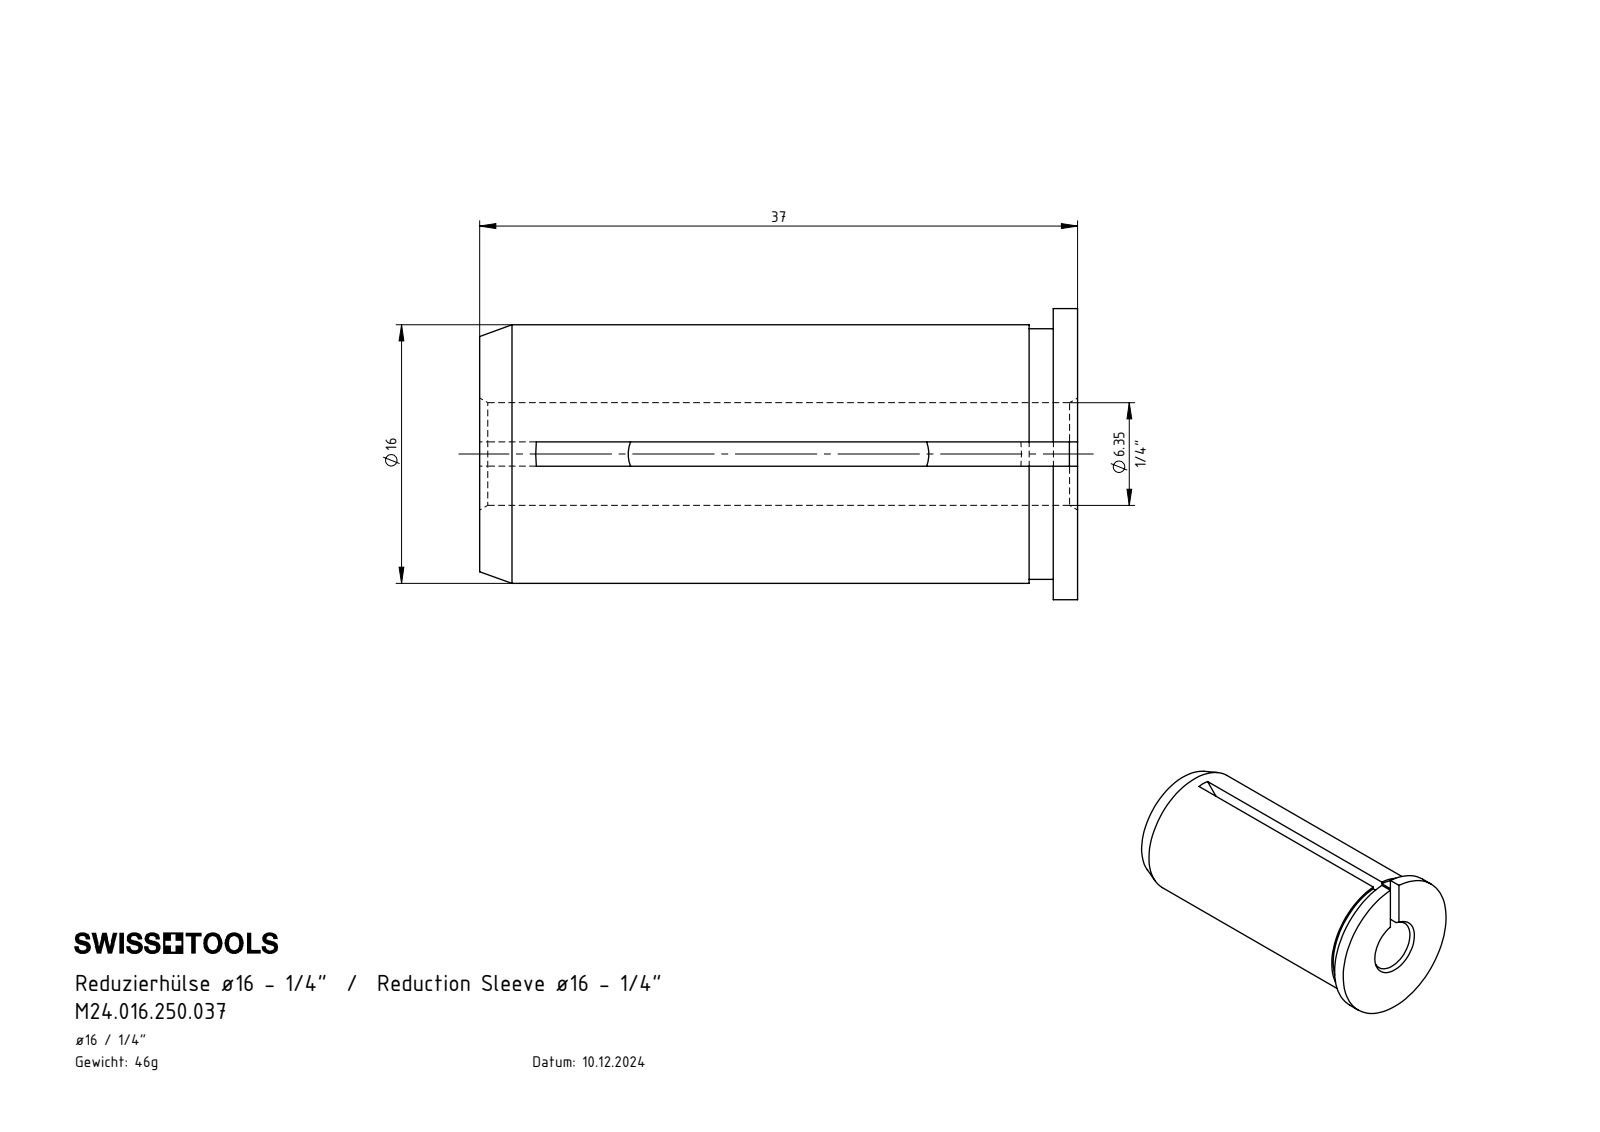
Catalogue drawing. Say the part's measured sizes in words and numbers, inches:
The part is named "M24.016.250.037". Its 3-D file was written by "SolidWorks 2022 (CONFIG_CONTROL_DESIGN)". It is 1 solid with 29 faces: 8 planar, 12 cylindrical and 9 other. Overall it measures 1.457 by 0.709 by 0.707 inches. Its volume is 0.357 cubic inches and its surface area 5.358 square inches. Round holes: 1 of diameter 0.25. Round bosses or shafts: 1 of diameter 0.709, 1 of diameter 0.63, 1 of diameter 0.61. Partial cylindrical surfaces (rounded edges, fillets, slot ends): 2 of radius 1.24. The main face-to-face distances are 0.059, 1.457, 1.398, 1.339, 0.118.
